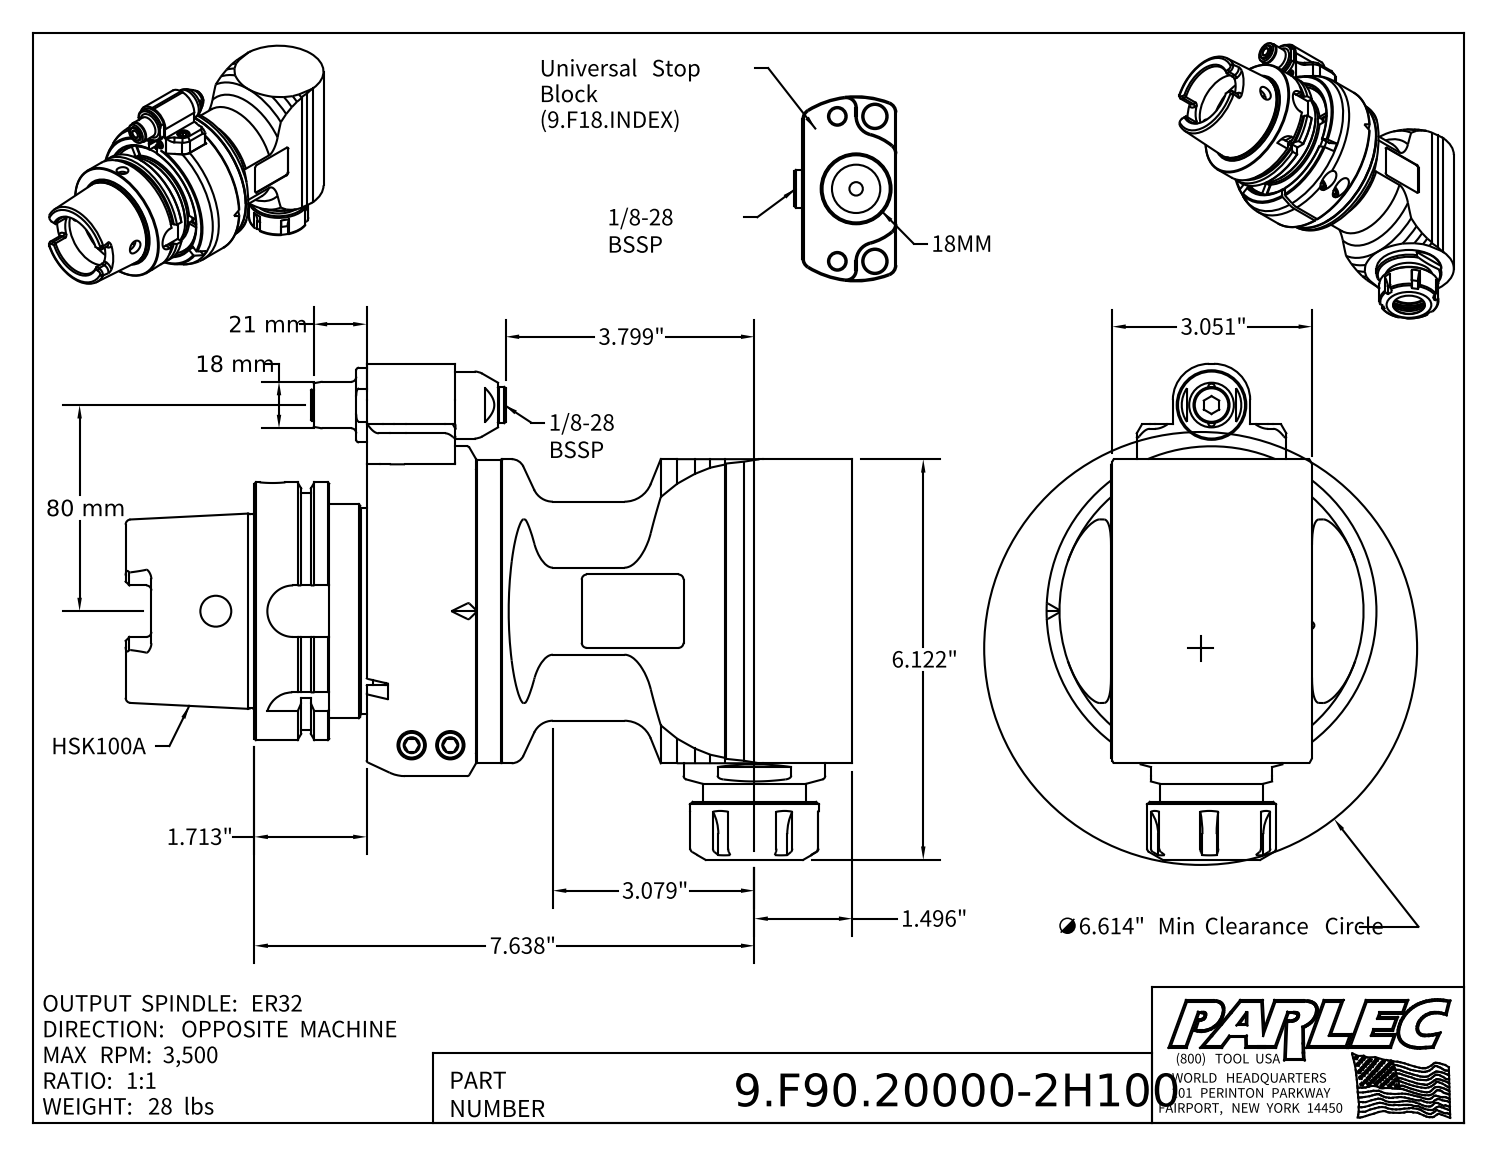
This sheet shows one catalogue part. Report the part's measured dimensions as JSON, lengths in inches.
{"part_name": "9.F90.20000-2H100; 9GA21C_518 (Type 2, HSK100 , 80mm); 9_F90_20000", "step_written_by": "Autodesk Inventor 2022 (AUTOMOTIVE_DESIGN)", "units": "inches", "bodies": {"solids": 4, "faces": 639, "planar": 288, "cylindrical": 170, "other": 181}, "overall_size": [11.102, 7.579, 5.039], "volume_in3": 123.5, "surface_area_in2": 339.8, "round_holes": [[0.197, 3], [0.256, 3], [0.492, 3], [1.063, 3], [0.102, 2], [0.13, 2], [0.165, 2], [0.315, 2], [0.409, 2], [0.433, 2], [0.098, 1], [0.118, 1]], "round_bosses_or_shafts": [[0.394, 4], [0.472, 3], [0.709, 2], [0.236, 2], [0.098, 2], [5.039, 1], [4.646, 1], [4.63, 1]], "partial_cylinders_radius": [[0.079, 18], [0.039, 14], [0.118, 6], [0.591, 6], [0.157, 4], [0.192, 4], [0.394, 4], [0.02, 2]], "face_to_face_distances": [1.378, 3.071, 0.197, 0.039, 0.02, 1.673, 1.339, 0.276, 1.575, 1.713], "hole_center_spacings": [0.276, 0.504, 0.74, 0.996, 2.5, 0.551, 0.591, 0.63]}
